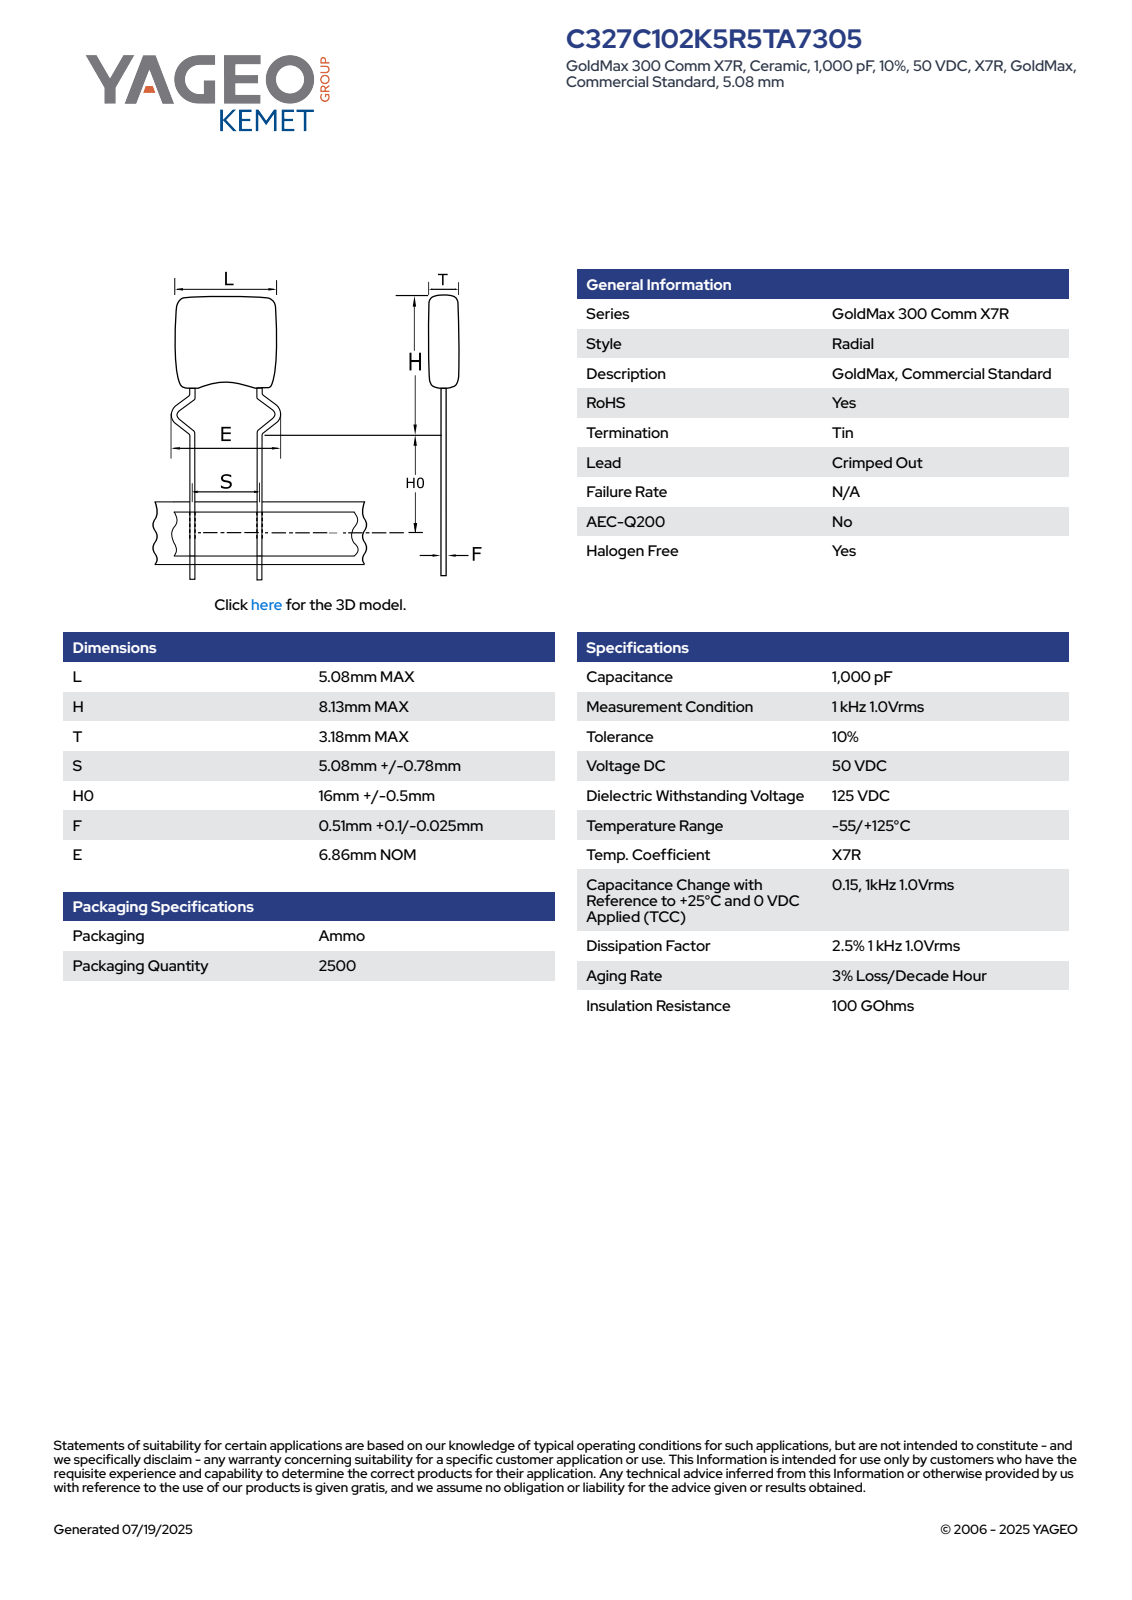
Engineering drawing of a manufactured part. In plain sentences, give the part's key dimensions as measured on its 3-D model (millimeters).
The part is named "CCR_RCCRTAPE_C327_L5.08H8.13T3.18S5.08H016.5F0.51E6.86". Its 3-D file was written by "SolidWorks 2014 (AUTOMOTIVE_DESIGN)". It is 4 solids with 104 faces: 66 planar, 16 cylindrical and 22 other. Overall it measures 24.63 by 6.86 by 3.19 millimeters. Its volume is 87 cubic millimeters and its surface area 175 square millimeters. Round bosses or shafts: 2 of diameter 0.51. Partial cylindrical surfaces (rounded edges, fillets, slot ends): 8 of radius 0.26, 4 of radius 0.75. The main face-to-face distances are 3.18, 5.08, 5.12, 3.19, 19.51, 24.63, 2.23, 2.89, 0.81, 22.4.
